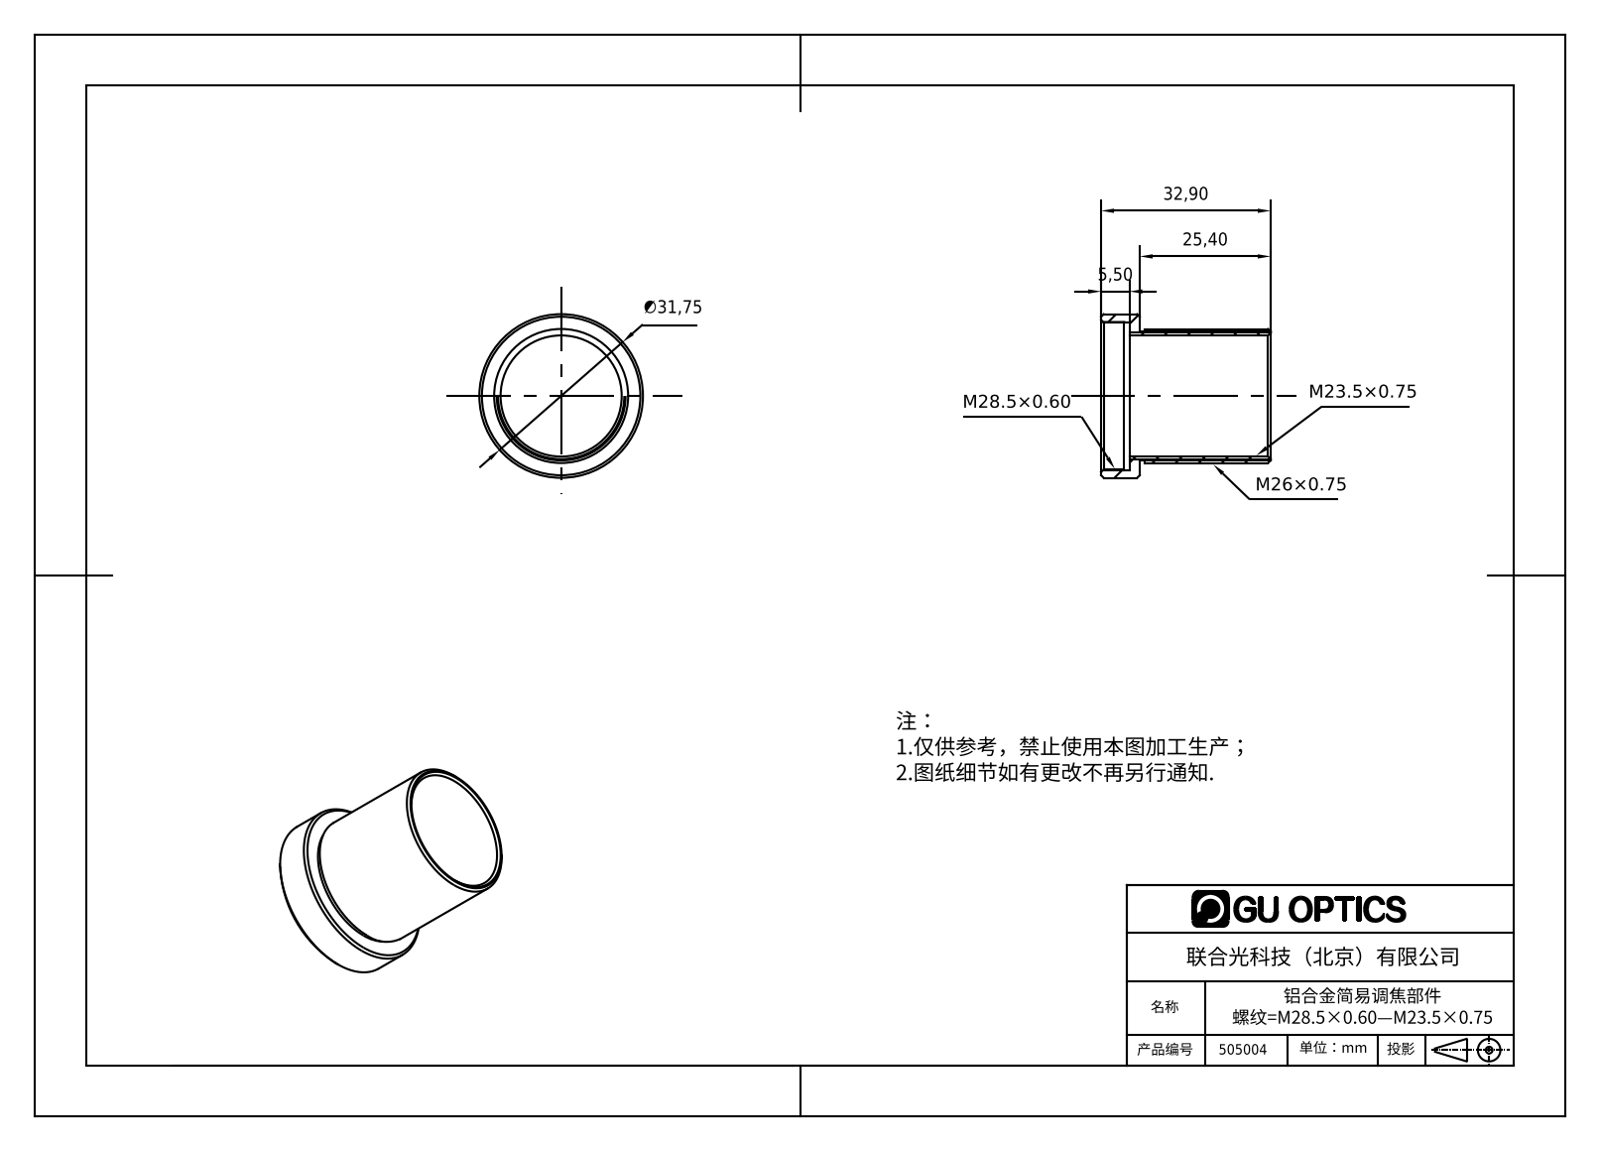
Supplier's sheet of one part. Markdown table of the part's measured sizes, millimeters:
| quantity | value |
| --- | --- |
| part name | 505004 |
| STEP written by | SolidWorks 2016 (CONFIG_CONTROL_DESIGN) |
| units | millimeters |
| bodies | 1 solid, 28 faces (6 planar, 12 cylindrical, 10 other) |
| overall size | 32.9 × 31.75 × 31.75 |
| volume | 3 926 mm³ |
| surface area | 6 019 mm² |
| round holes (diameter × count) | 23.5 × 1, 28.5 × 1, 28.7 × 1 |
| round bosses / shafts (diameter × count) | 31.75 × 1, 26 × 1, 25 × 1 |
| main face-to-face distances | 2, 5.5, 7.5, 1, 3, 8.5, 32.9, 27.4, 25.4, 24.4 |
